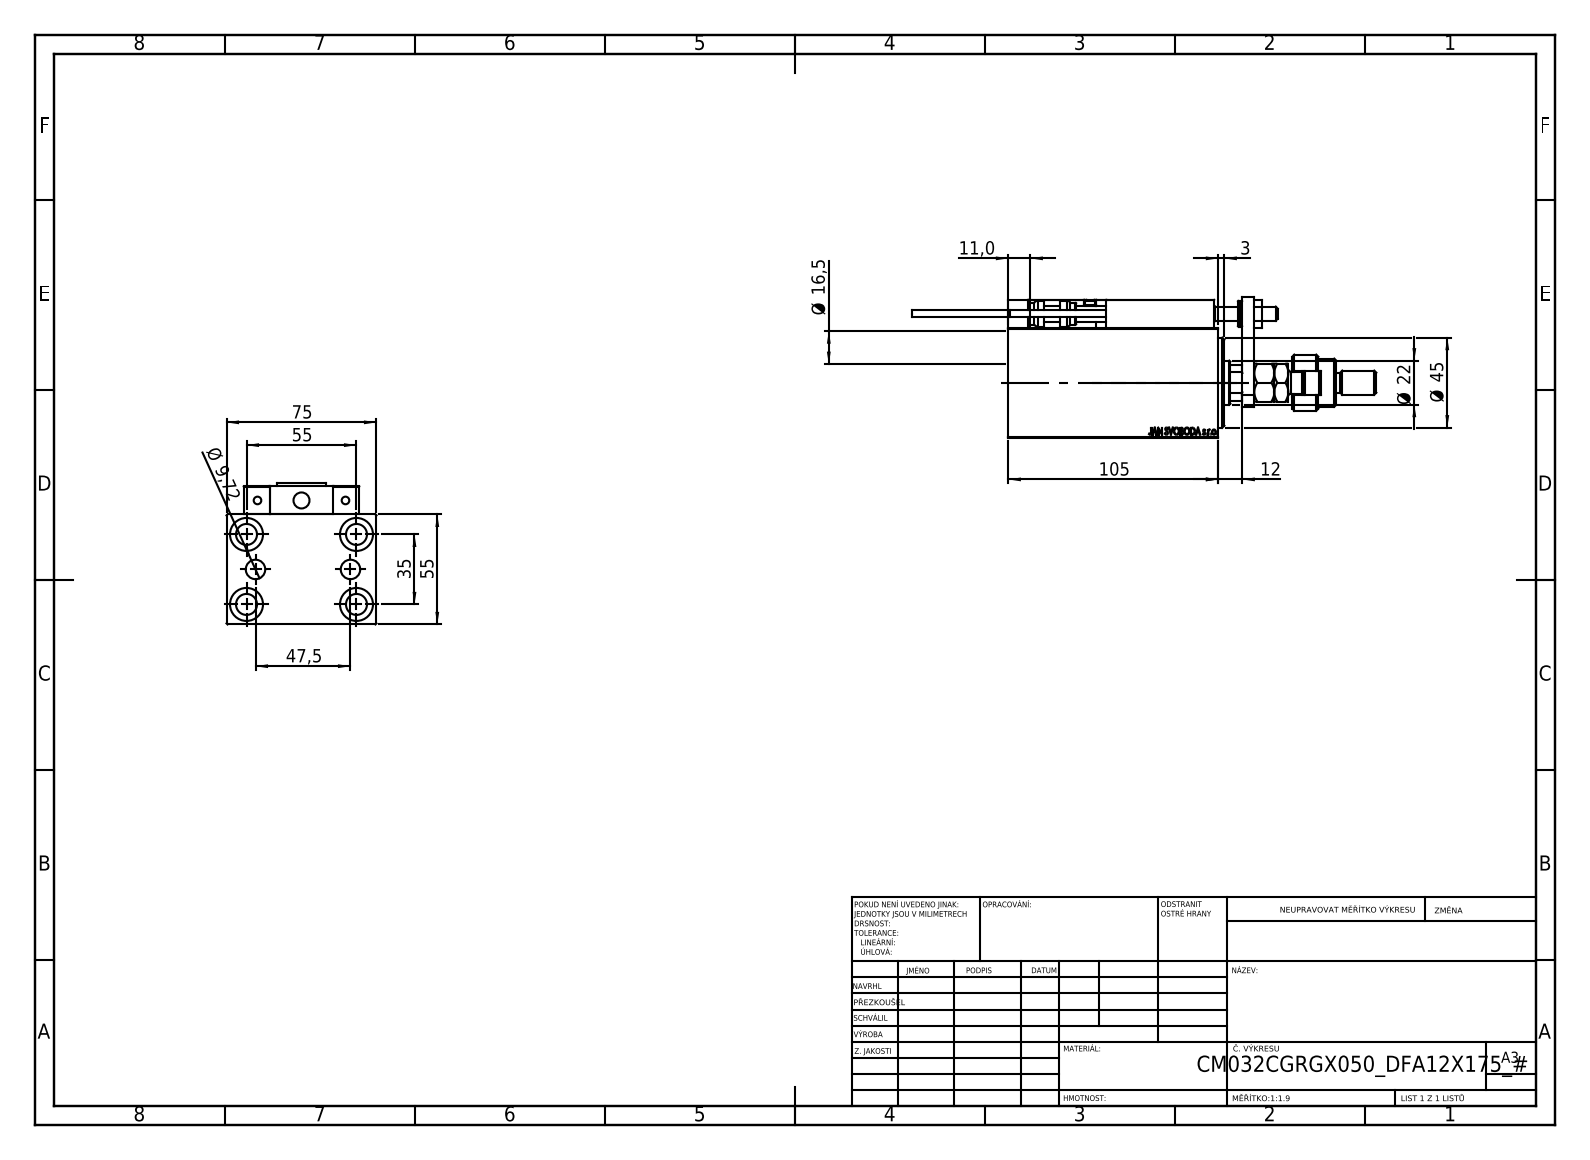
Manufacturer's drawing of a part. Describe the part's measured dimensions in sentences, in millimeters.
The part is named "FEMALE_PART_FOR_DFA; V450CM_C_VCP; MFA; Block (+7 more)". Its 3-D file was written by "SolidWorks 2019 (CONFIG_CONTROL_DESIGN)". It is 25 solids with 1357 faces: 586 planar, 193 cylindrical and 578 other. Overall it measures 232 by 75 by 70.5 millimeters. Its volume is 435 520 cubic millimeters and its surface area 108 553 square millimeters. Round holes: 5 of diameter 8, 5 of diameter 10.5, 5 of diameter 16.5, 4 of diameter 3.2, 4 of diameter 4, 2 of diameter 5, 2 of diameter 9.72, 1 of diameter 7, 1 of diameter 22, 1 of diameter 25.5, 1 of diameter 32, 1 of diameter 34. Round bosses or shafts: 2 of diameter 11, 2 of diameter 5, 2 of diameter 3.8, 1 of diameter 28, 1 of diameter 24, 1 of diameter 18, 1 of diameter 13, 1 of diameter 12. Partial cylindrical surfaces (rounded edges, fillets, slot ends): 30 of radius 0.3, 2 of radius 3, 1 of radius 9.75, 1 of radius 10.5. The main face-to-face distances are 55, 75, 14, 10, 12, 18, 25, 6, 69, 7. The hole center spacings are 32.6, 11.37, 17.76, 18.07, 20, 29.59, 29.69, 32.33.
